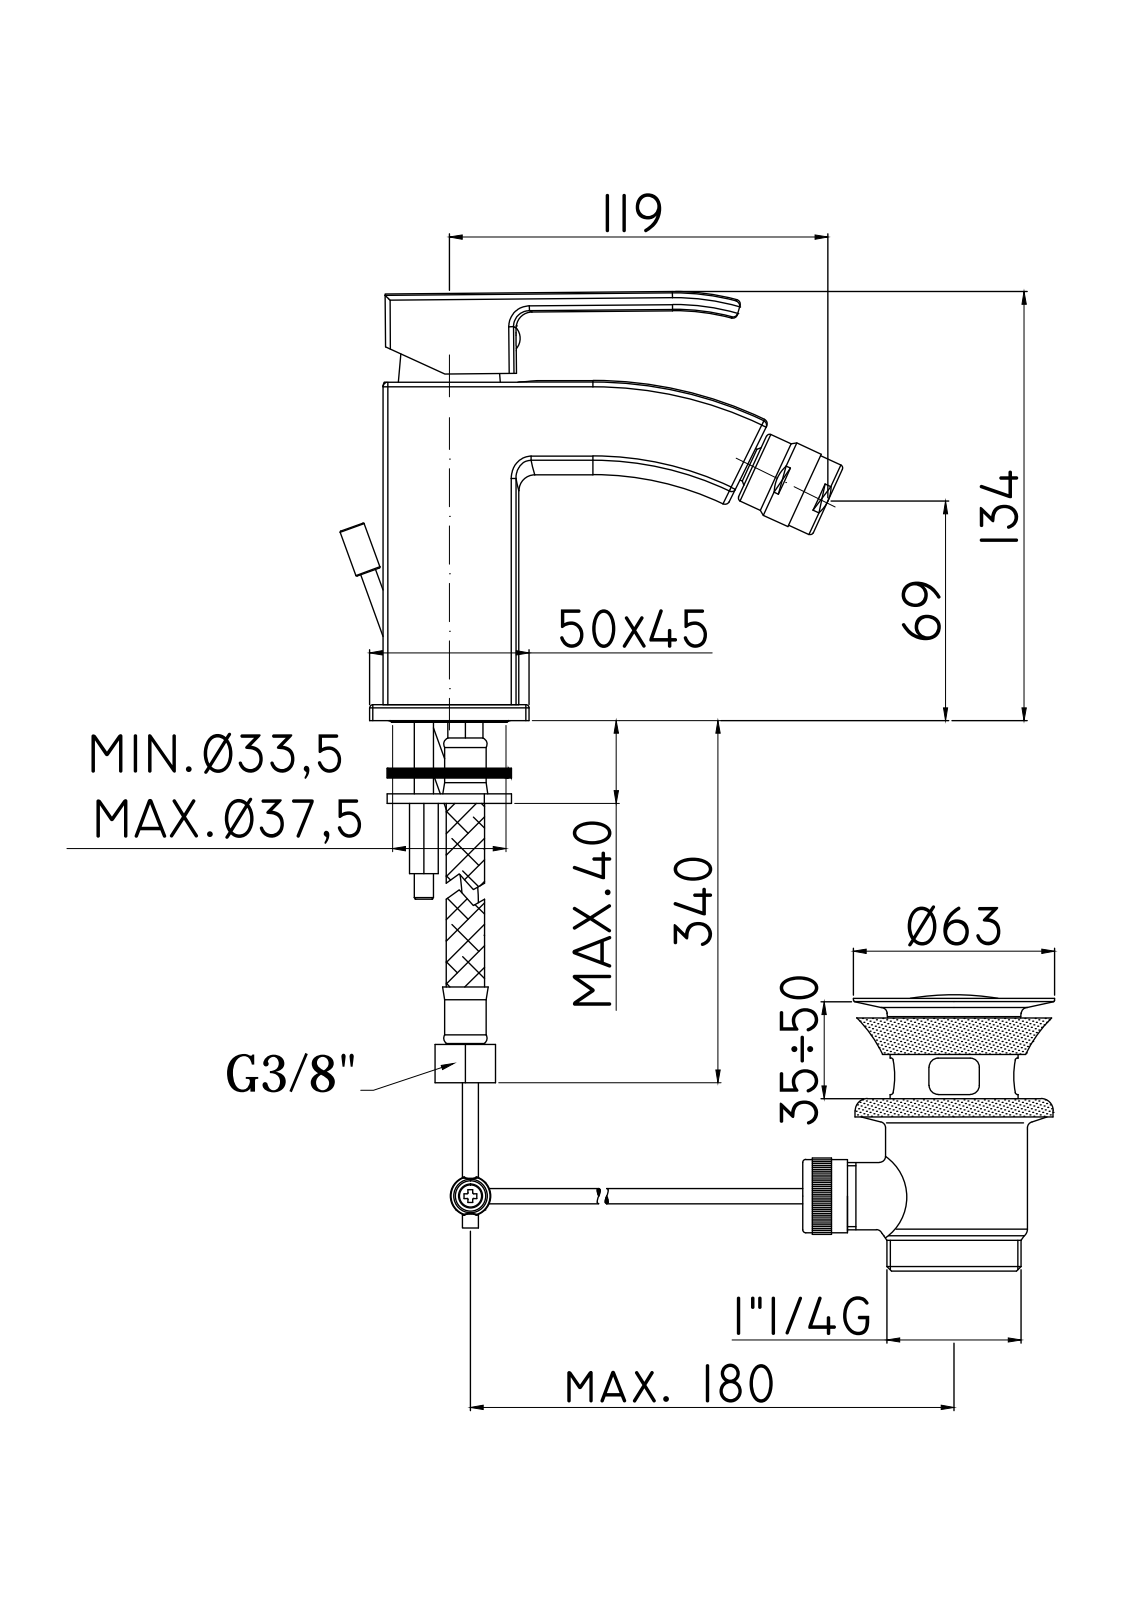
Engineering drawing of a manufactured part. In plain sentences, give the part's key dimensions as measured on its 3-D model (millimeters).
The part is named "LES135CR". Its 3-D file was written by "CREO PARAMETRIC BY PTC INC, 2020044 (CONFIG_CONTROL_DESIGN)". It is 6 solids with 2504 faces: 1735 planar, 402 cylindrical and 367 other. Overall it measures 158.78 by 134.03 by 45 millimeters. Its volume is 176 706 cubic millimeters and its surface area 92 045 square millimeters. Round holes: 3 of diameter 5, 2 of diameter 4.6, 2 of diameter 6.2, 2 of diameter 9, 2 of diameter 11, 1 of diameter 3, 1 of diameter 4.2, 1 of diameter 5.5, 1 of diameter 7.8, 1 of diameter 8, 1 of diameter 15.5, 1 of diameter 16. Round bosses or shafts: 3 of diameter 5, 2 of diameter 24, 2 of diameter 10.8, 2 of diameter 6, 2 of diameter 4, 1 of diameter 38.8, 1 of diameter 31.5, 1 of diameter 30. Partial cylindrical surfaces (rounded edges, fillets, slot ends): 56 of radius 0.5, 26 of radius 1.5, 25 of radius 1, 16 of radius 2, 10 of radius 0.7, 6 of radius 0.8, 4 of radius 0.6, 4 of radius 0.65. The main face-to-face distances are 3.75, 32.75, 36.5, 29, 5, 3, 0.75, 35.75, 32, 33.5. The hole center spacings are 2.76, 6.72, 9.01, 12.25, 13.46, 13.6, 14.2, 20.26.
